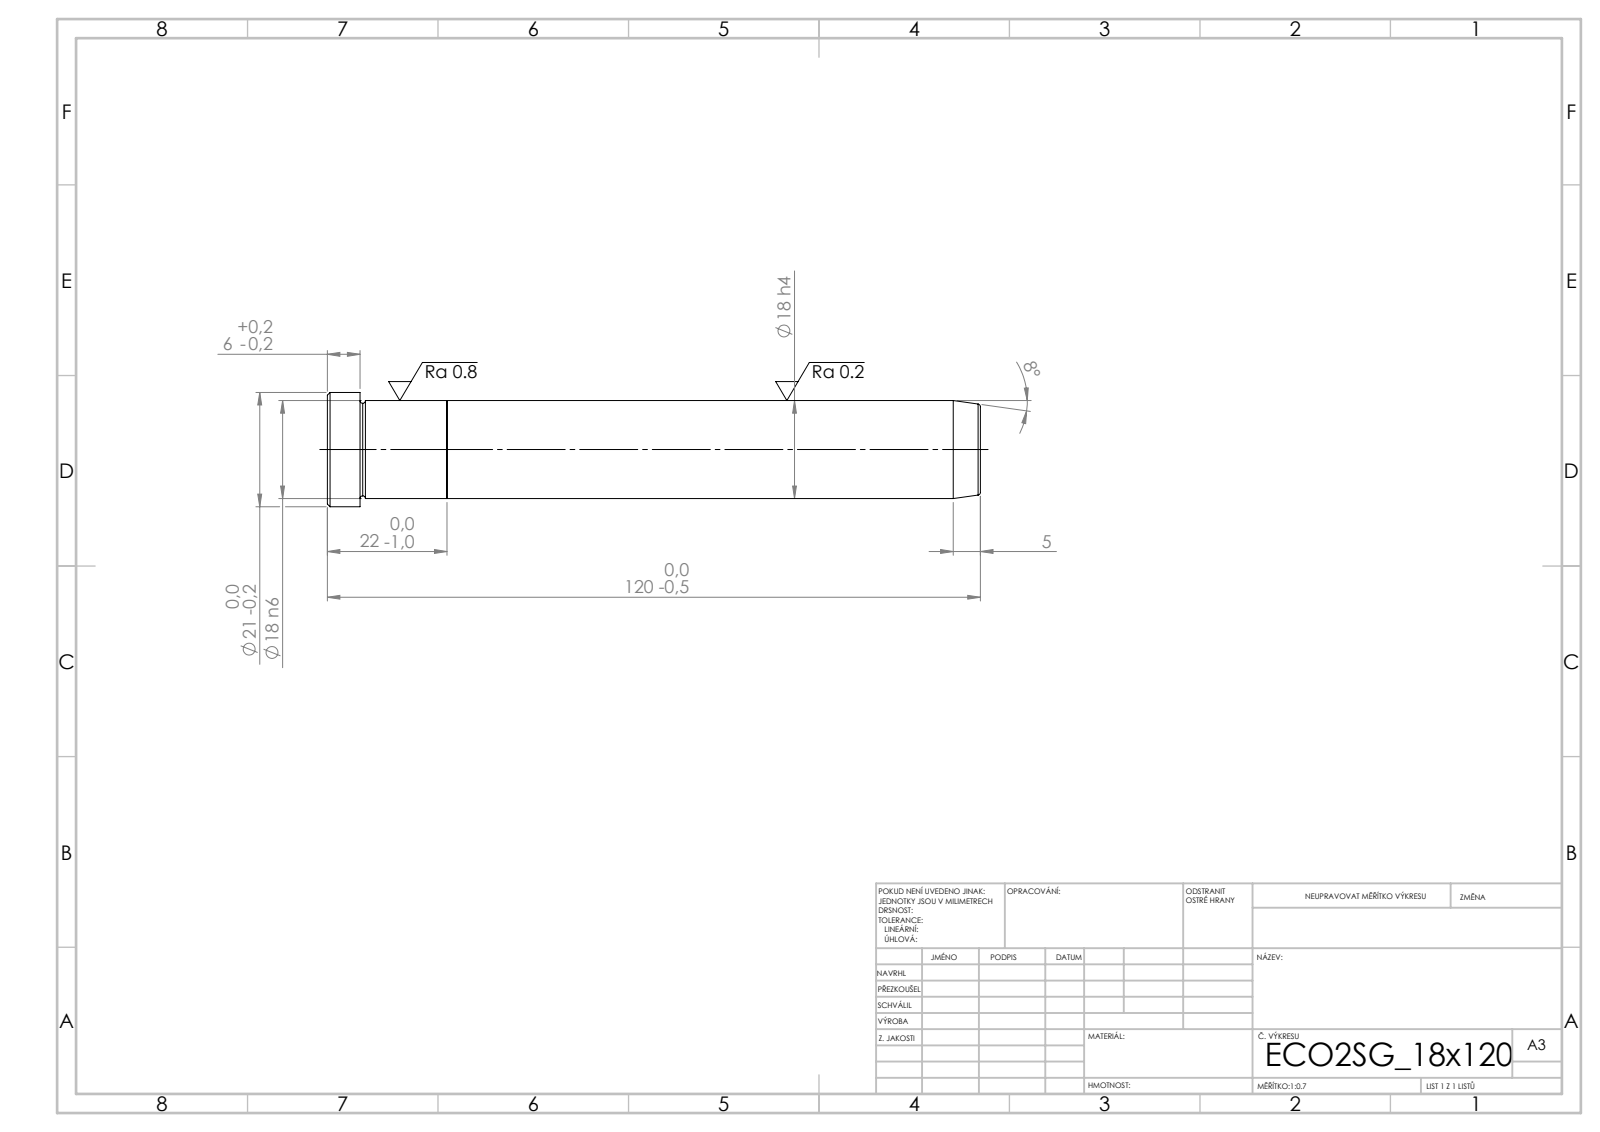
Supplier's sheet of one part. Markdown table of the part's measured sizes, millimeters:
| quantity | value |
| --- | --- |
| STEP written by | SolidWorks 2019 (CONFIG_CONTROL_DESIGN) |
| units | millimeters |
| bodies | 2 solids, 21 faces (5 planar, 6 cylindrical, 10 other) |
| overall size | 120 × 21 × 21 |
| volume | 30 959 mm³ |
| surface area | 7 999 mm² |
| round bosses / shafts (diameter × count) | 21 × 1, 18 × 1 |
| main face-to-face distances | 22, 98, 120, 114, 16, 6 |
